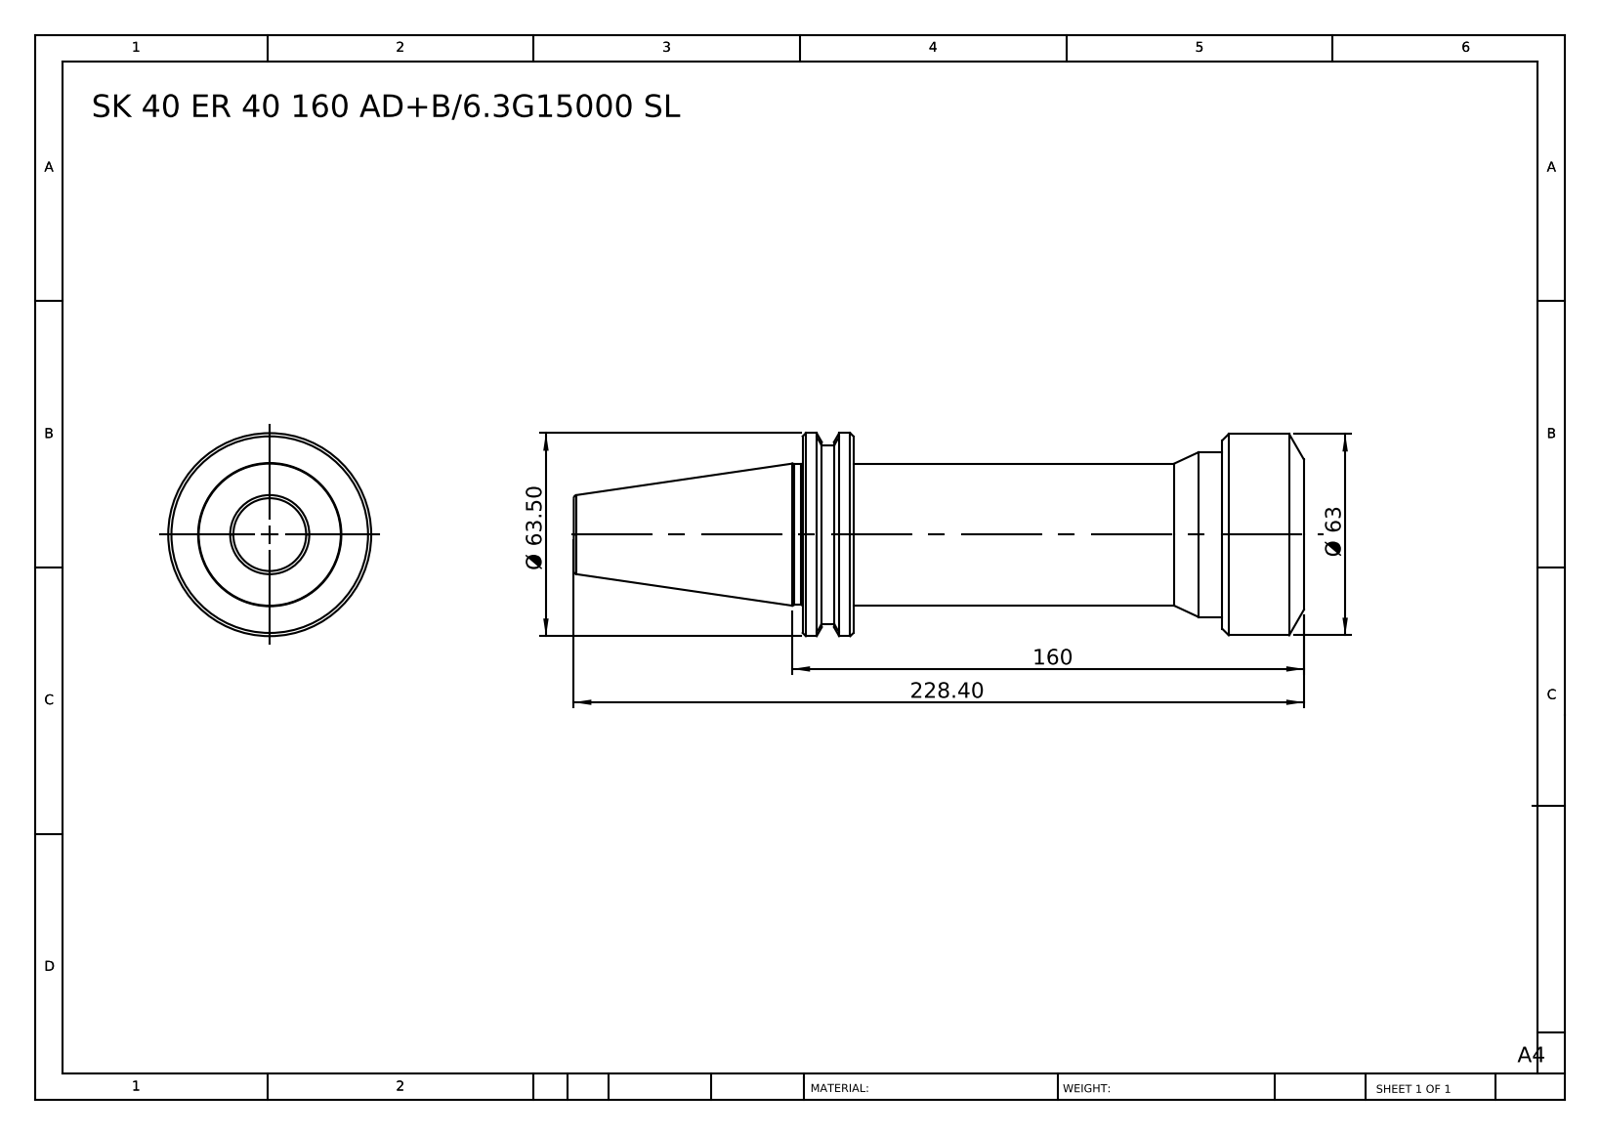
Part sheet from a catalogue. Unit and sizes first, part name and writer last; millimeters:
Units: millimetres
Overall size (bounding box): 228.4 × 63.5 × 63.5
Round bosses / shafts (diameter × count): ⌀63.5 ×1, ⌀63 ×1, ⌀56 ×1, ⌀51.5 ×1, ⌀44.5 ×1, ⌀44 ×1
Main face-to-face distances: 140.9, 156.8, 15.9, 25.5, 115.4, 131.3, 228.4, 202.9, 87.5, 71.6
Volume: 378 233 mm³ · Surface area: 40 150 mm²
Bodies: 1 solid, 53 faces (7 planar, 14 cylindrical, 32 other)
Part name (STEP PRODUCT): SK 40 ER 40 160 AD-6.3G15000 SL
STEP written by: SolidWorks 2014 (CONFIG_CONTROL_DESIGN)
